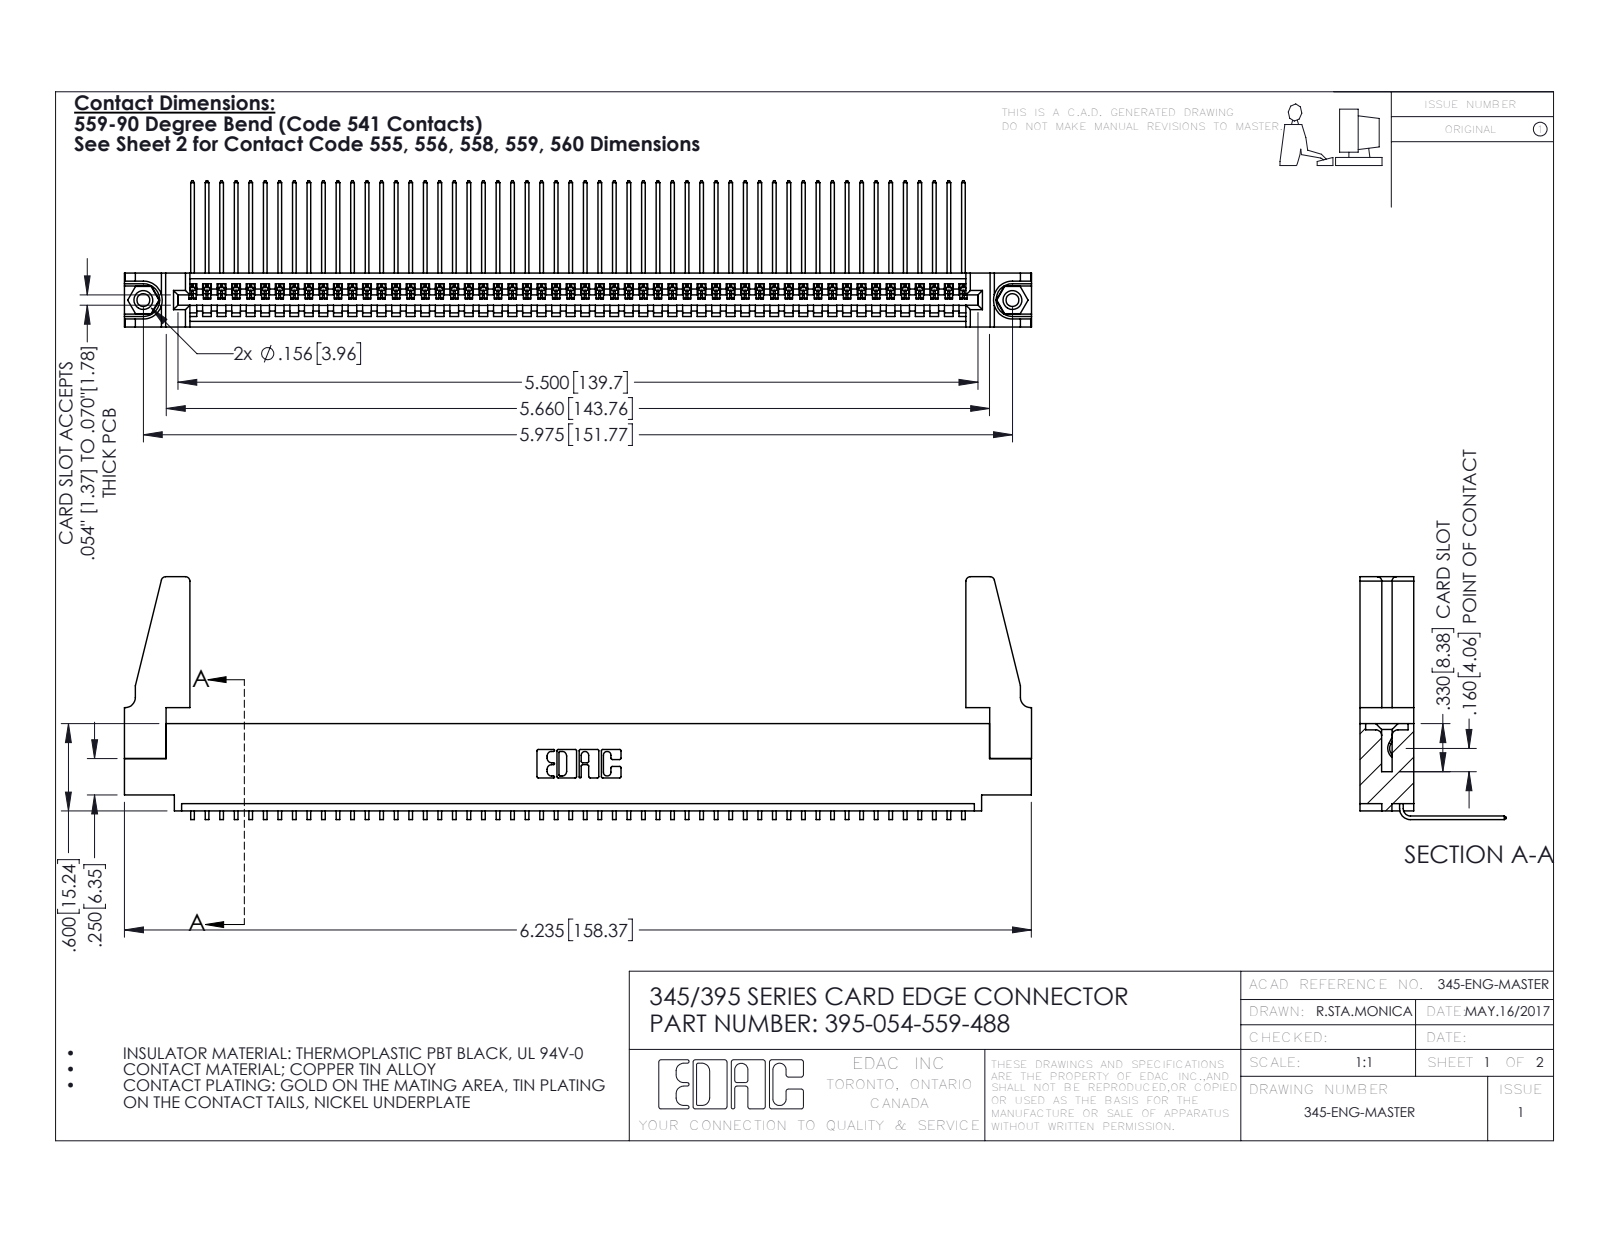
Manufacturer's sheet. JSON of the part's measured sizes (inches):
{"part_name": "345 Part_0.110 Offset - 0.156 Dia-TH; 345-250-001_345-250-001-102; 345-292-001_558 559 Tail - 1; 395-054-559-488 (+1 more)", "step_written_by": "SolidWorks 2016 (CONFIG_CONTROL_DESIGN)", "units": "inches", "bodies": {"solids": 59, "faces": 3494, "planar": 2424, "cylindrical": 1054, "other": 16}, "overall_size": [6.236, 1.669, 1.005], "volume_in3": 1.129, "surface_area_in2": 38.28, "round_holes": [[0.089, 2], [0.125, 2], [0.156, 2], [0.064, 1]], "round_bosses_or_shafts": [[0.155, 2]], "partial_cylinders_radius": [[0.006, 108], [0.01, 22], [0.03, 8], [0.007, 6], [0.031, 6], [0.026, 3], [0.031, 2], [0.04, 2]], "face_to_face_distances": [0.072, 0.298, 0.37, 0.2, 0.098, 0.272, 0.025, 0.225, 0.149, 0.072], "hole_center_spacings": [0.27, 5.739, 5.975]}
